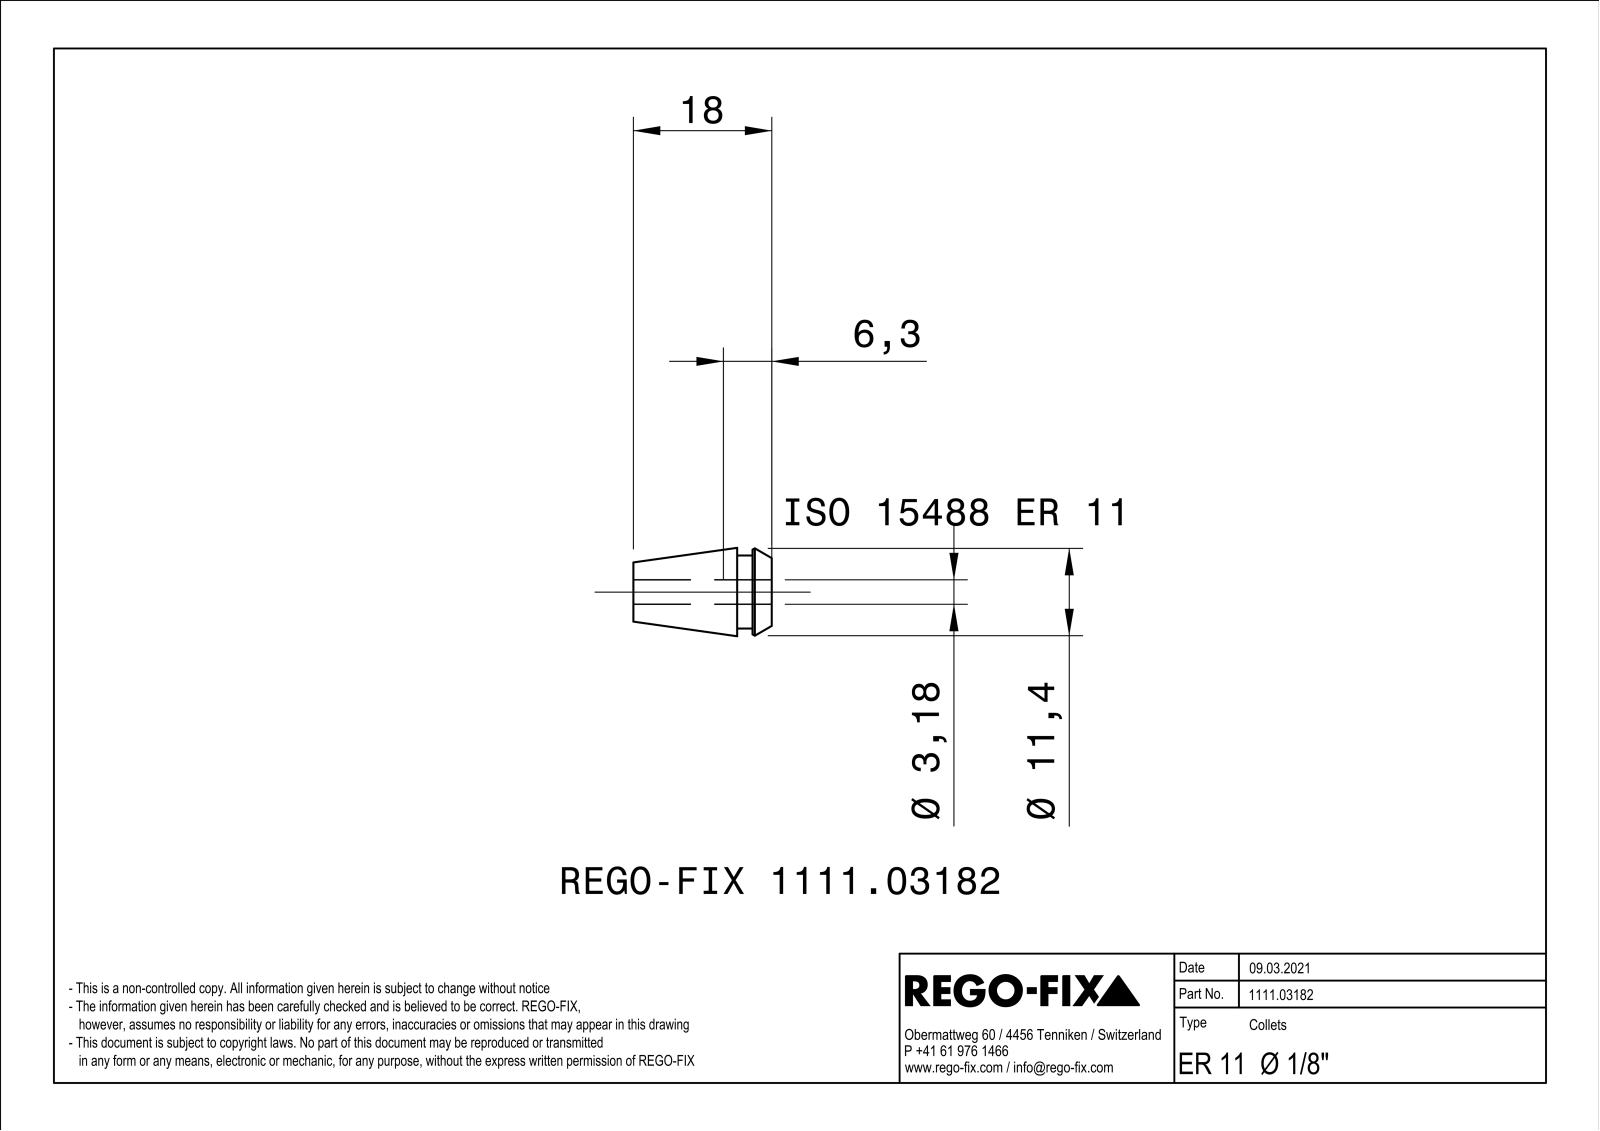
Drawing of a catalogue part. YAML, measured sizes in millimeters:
part_name: "NOCUT"
step_written_by: "SIEMENS PLM Software Solid Edge ST10 (AUTOMOTIVE_DESIGN)"
units: millimeters
bodies: {solids: 1, faces: 157, planar: 66, cylindrical: 37, other: 54}
overall_size: [18, 11.5, 11.49]
volume: 944
surface_area: 1859
round_holes:
  - {diameter: 3.17, count: 1}
round_bosses_or_shafts:
  - {diameter: 11.5, count: 1}
  - {diameter: 9.5, count: 1}
partial_cylinders:
  - {radius: 25, count: 12}
face_to_face_distances: [0.45, 0.46, 0.44, 2.5, 18, 15.5, 4.5, 2, 13.5, 4]
